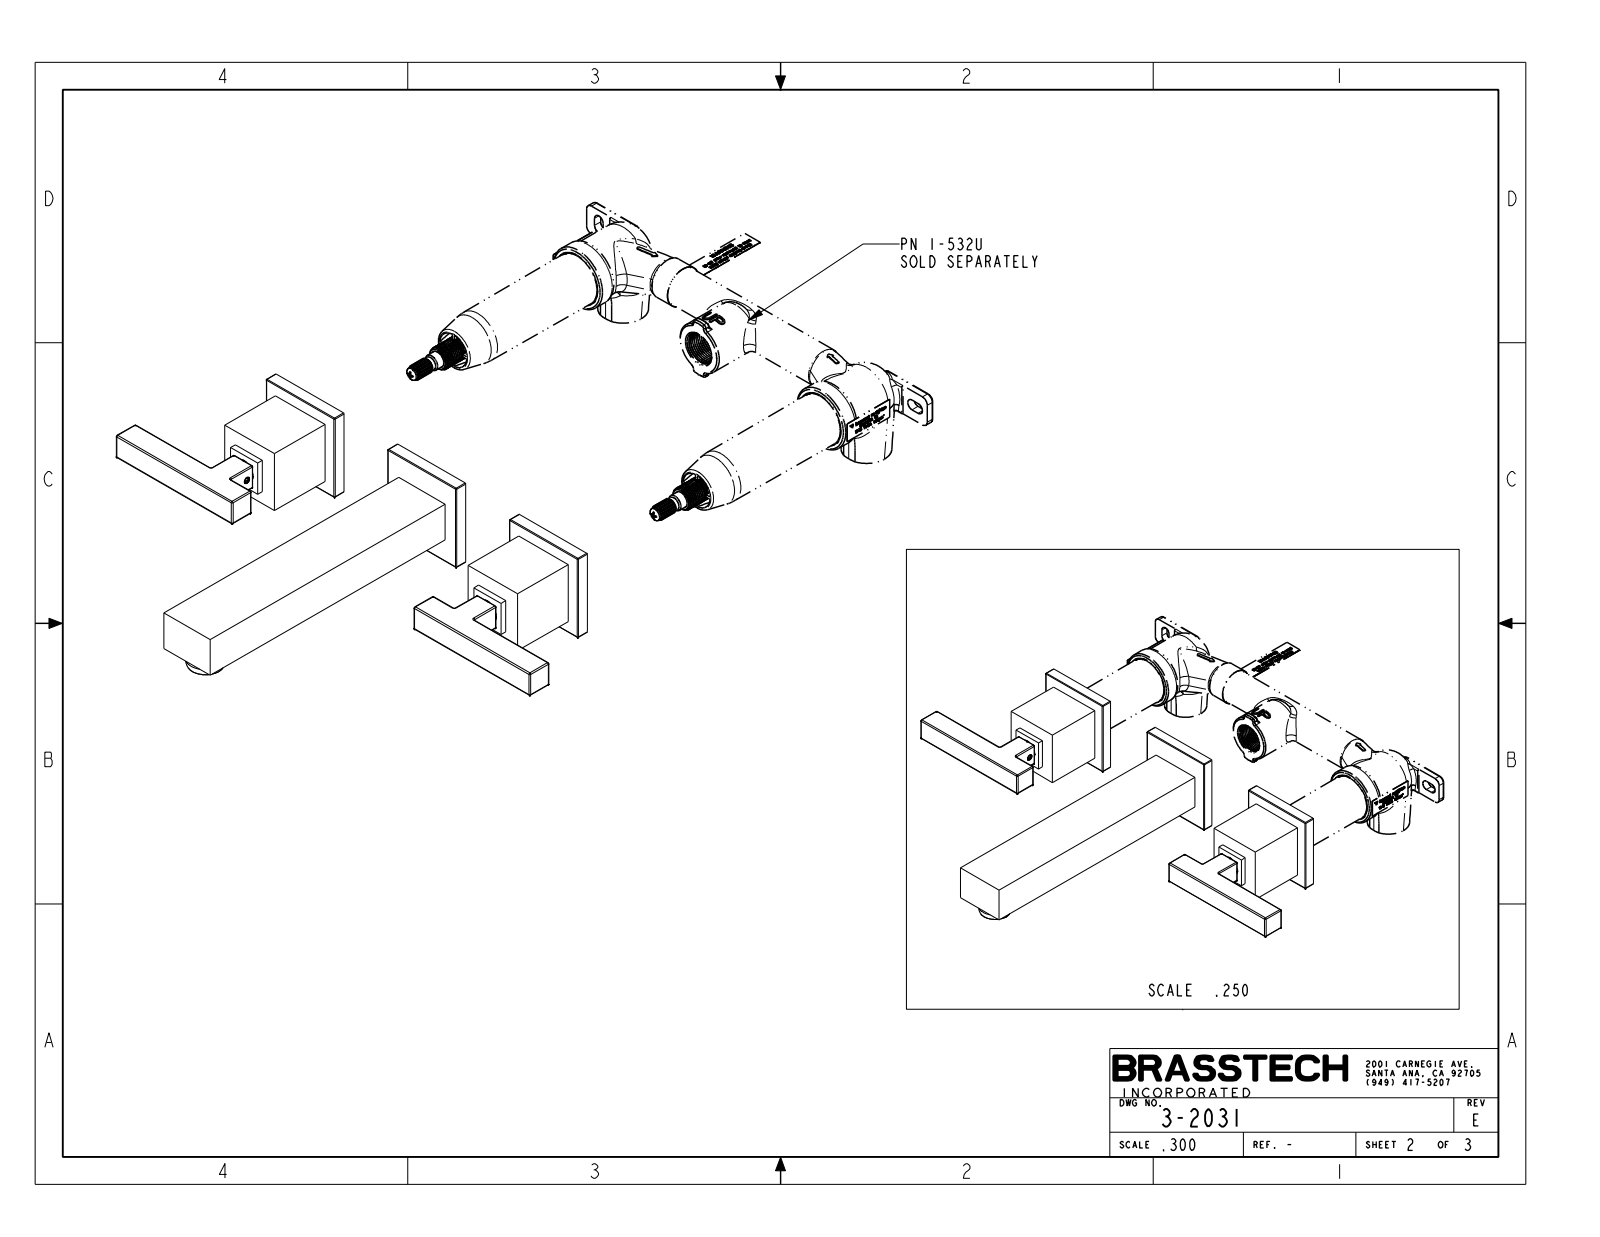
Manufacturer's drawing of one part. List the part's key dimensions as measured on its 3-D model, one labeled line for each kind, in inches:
Part name (STEP PRODUCT): 3-2031_SW
STEP written by: CREO PARAMETRIC BY PTC INC, 2018400 (AUTOMOTIVE_DESIGN)
Units: inches
Bodies: 3 solids, 211 faces (71 planar, 92 cylindrical, 48 other)
Overall size (bounding box): 13.394 × 7.91 × 2.22
Volume: 28.33 in³ · Surface area: 125.9 in²
Round holes (diameter × count): ⌀1.535 ×2
Round bosses / shafts (diameter × count): ⌀1.315 ×2, ⌀0.8 ×2, ⌀0.925 ×1, ⌀0.88 ×1, ⌀0.553 ×1, ⌀0.517 ×1
Partial cylindrical surfaces — rounded edges, fillets, slot ends (radius × count): R0.03 ×38, R0.02 ×20
Main face-to-face distances: 0.31, 0.487, 1.113, 1, 1.6, 0.3, 1.3, 0.187, 0.813, 1.5
Hole centre spacings: 7.874
